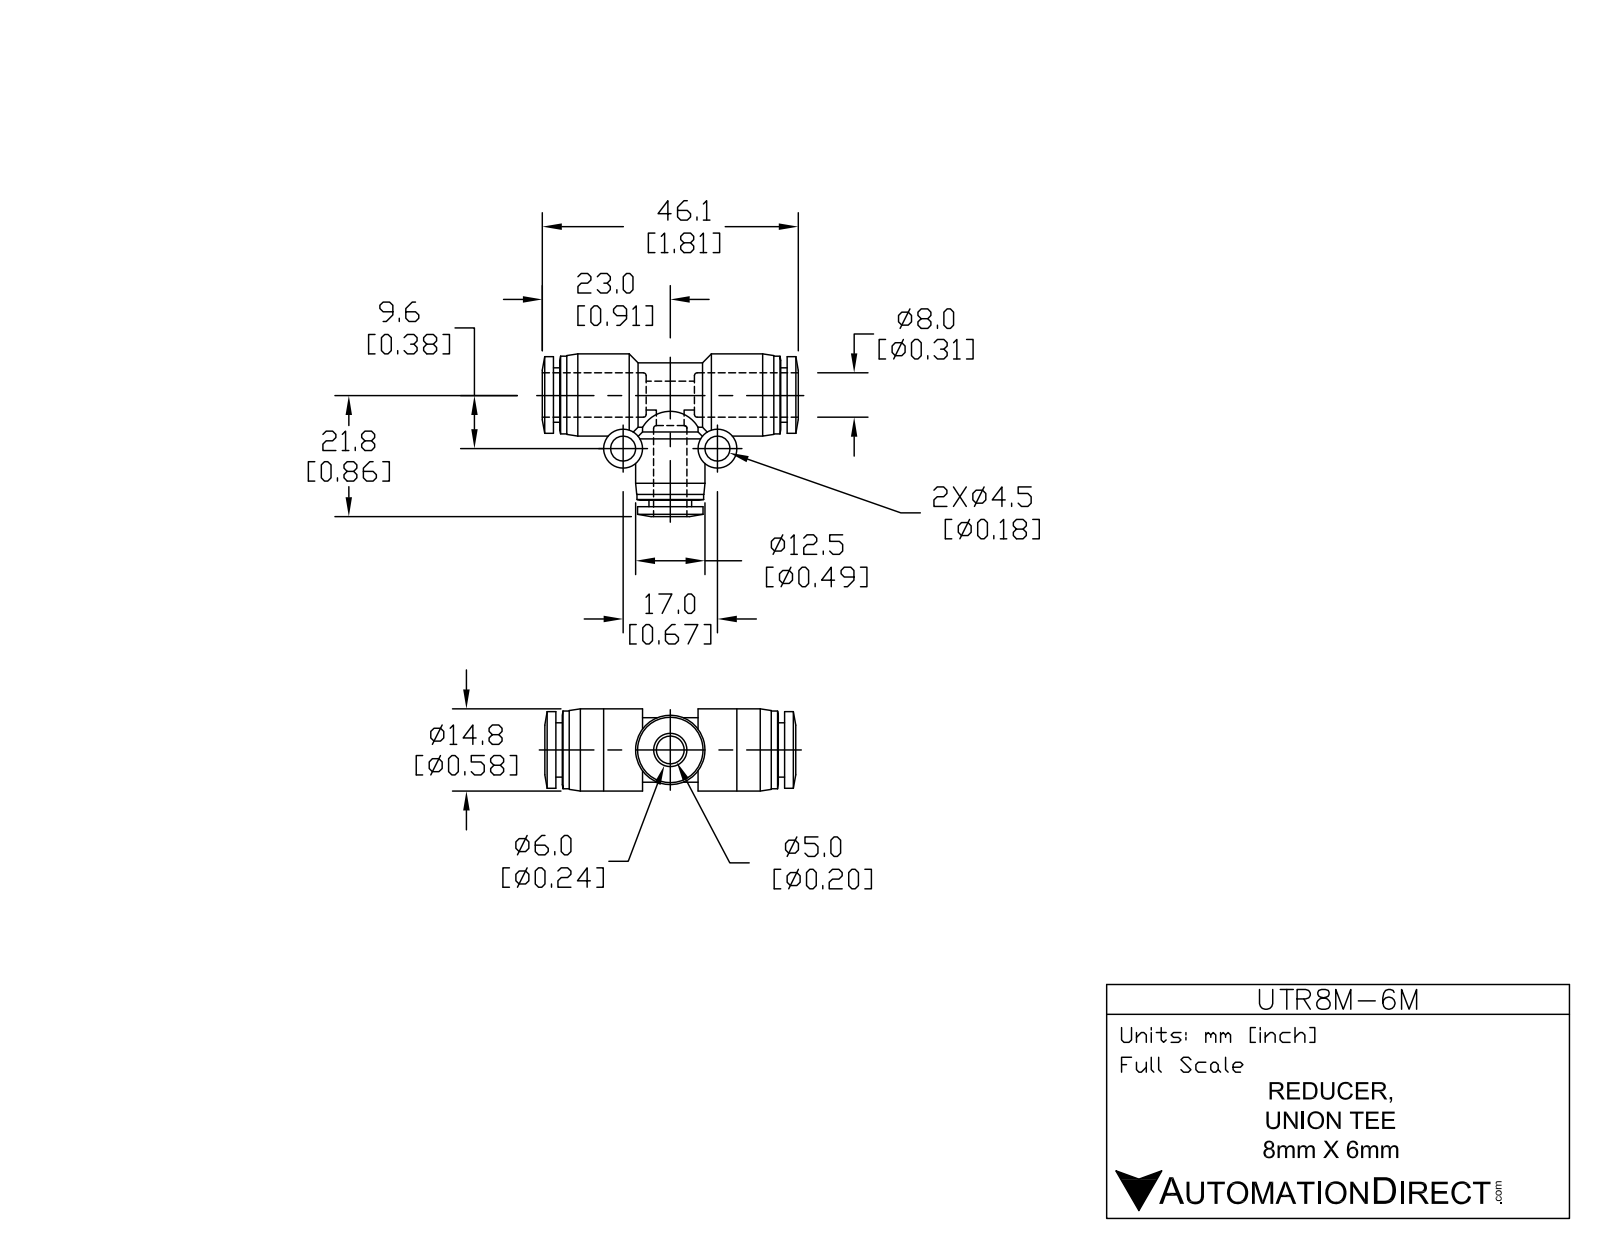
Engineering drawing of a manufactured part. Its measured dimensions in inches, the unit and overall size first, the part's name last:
Units: inches
Overall size (bounding box): 1.78 × 1.154 × 0.583
Round holes (diameter × count): ⌀0.177 ×2, ⌀0.197 ×2, ⌀0.248 ×1, ⌀0.327 ×1
Round bosses / shafts (diameter × count): ⌀0.276 ×2, ⌀0.583 ×1, ⌀0.551 ×1, ⌀0.543 ×1, ⌀0.492 ×1, ⌀0.472 ×1, ⌀0.465 ×1, ⌀0.457 ×1
Main face-to-face distances: 0.045, 1.577, 1.622, 0.642, 0.98, 0.596, 0.935, 1.531, 0.583, 0.339
Hole centre spacings: 0.669
Volume: 0.375 in³ · Surface area: 8.683 in²
Bodies: 1 solid, 95 faces (19 planar, 46 cylindrical, 30 other)
Part name (STEP PRODUCT): UTR8M-6M
STEP written by: SolidWorks 2015 (AUTOMOTIVE_DESIGN)
